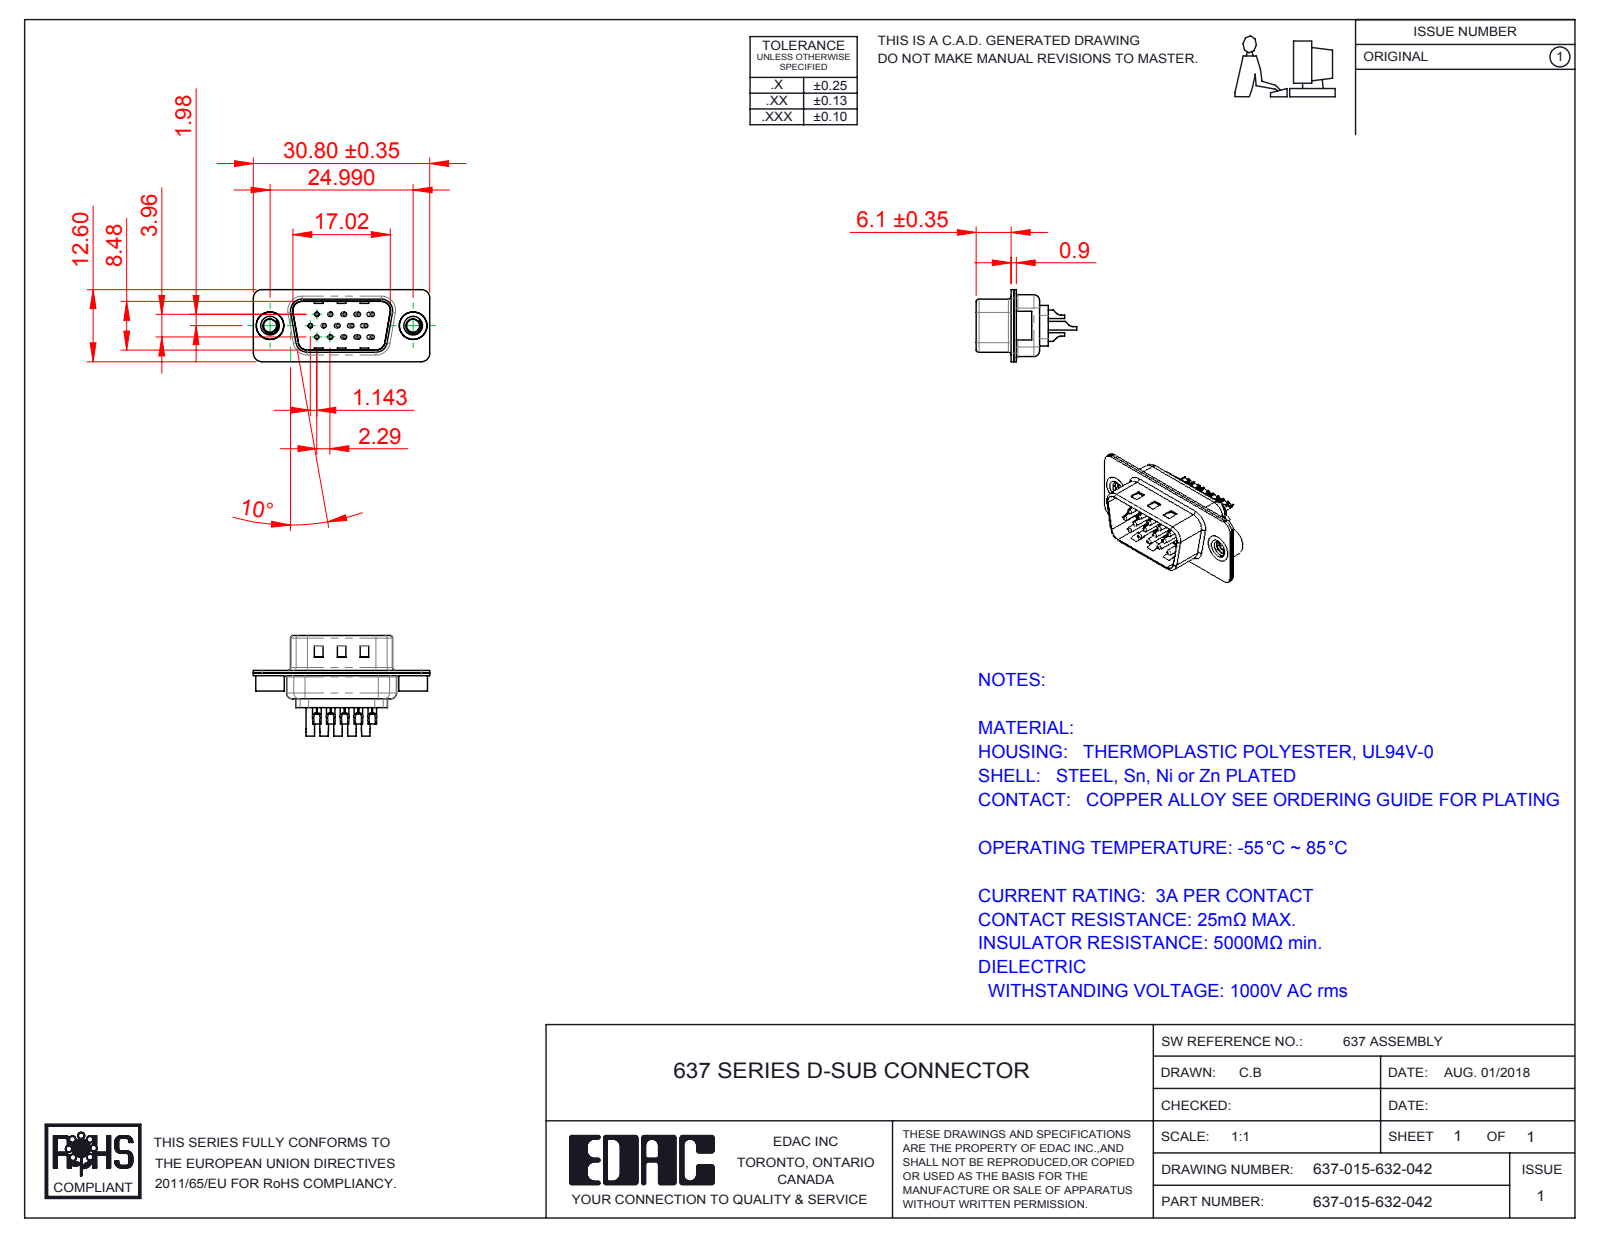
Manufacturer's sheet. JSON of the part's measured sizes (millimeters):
{"part_name": "637 4-40 Threaded Rivet; 637 Housing_15 Contacts; 637 Shell Rear_15 Contacts; 637 Shell Front_15 Contacts (+4 more)", "step_written_by": "SolidWorks 2016 (CONFIG_CONTROL_DESIGN)", "units": "millimeters", "bodies": {"solids": 20, "faces": 1264, "planar": 317, "cylindrical": 564, "other": 383}, "overall_size": [30.8, 17.55, 12.6], "volume_mm3": 1332, "surface_area_mm2": 4779, "round_holes": [[1.6, 27], [0.35, 15], [1.1, 15], [0.75, 12], [2, 12], [2.26, 2], [4, 2], [4.8, 2]], "round_bosses_or_shafts": [[2, 15], [1.5, 15], [0.75, 15], [5, 2], [4.9, 2]], "partial_cylinders_radius": [[1.5, 16], [2, 12], [0.5, 8], [1, 7], [0.25, 4], [0.55, 4], [0.7, 4], [0.95, 4]], "face_to_face_distances": [0.45, 0.9, 0.4, 0.7, 8.48, 8.88, 0.31, 4.55, 1.05, 1.16], "hole_center_spacings": [3.96, 2.29, 2.28, 4.57, 2.42, 6.05, 4.84, 2.35]}
